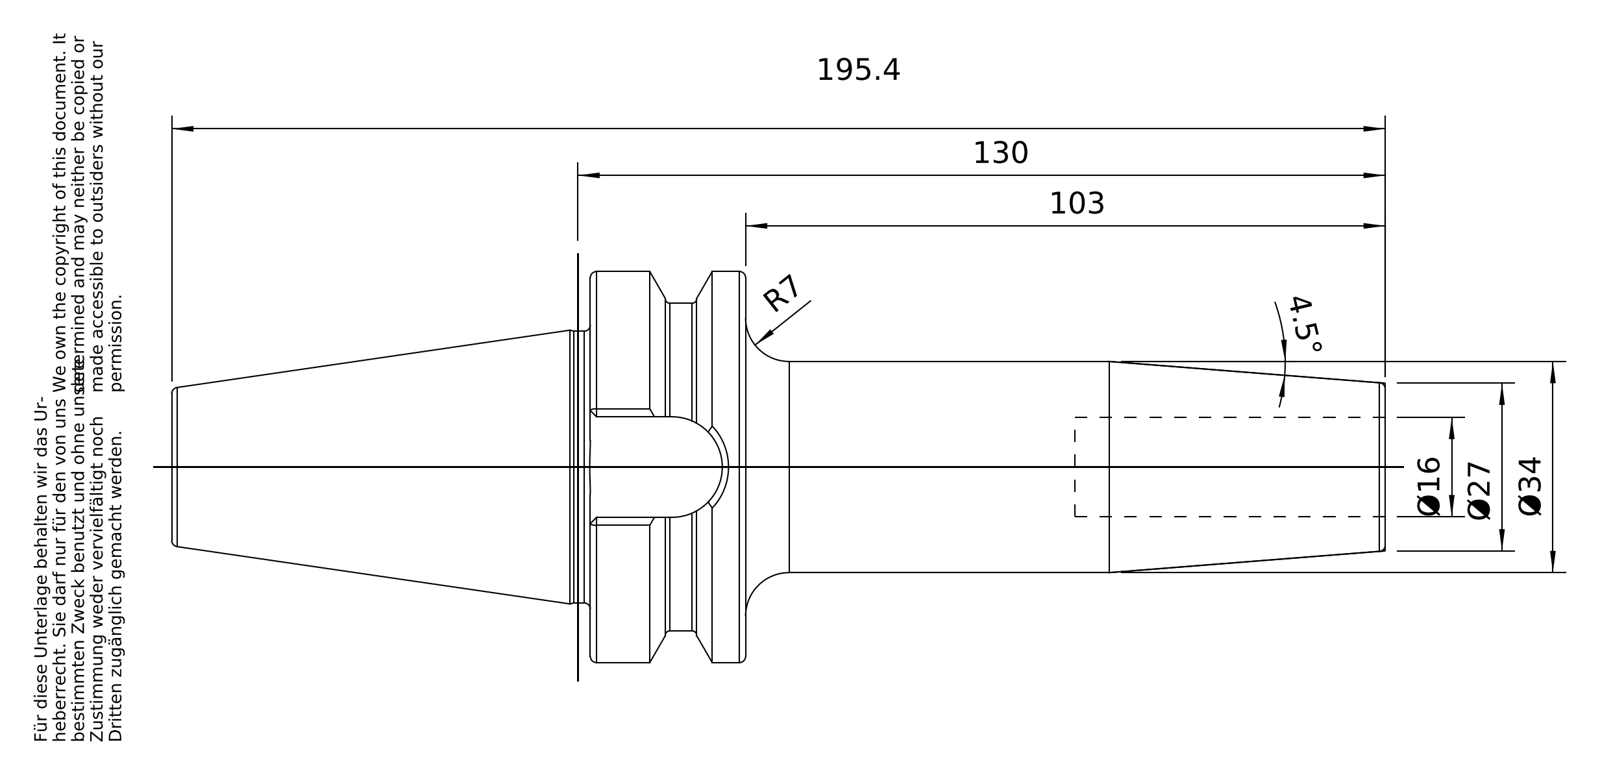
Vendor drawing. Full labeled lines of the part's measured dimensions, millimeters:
Part name (STEP PRODUCT): 40-644-16
STEP written by: PRO/ENGINEER BY PARAMETRIC TECHNOLOGY CORPORATION, 2010430 (CONFIG_CONTROL_DESIGN)
Units: millimetres
Bodies: 1 solid, 96 faces (26 planar, 22 cylindrical, 48 other)
Overall size (bounding box): 195.4 × 62.98 × 62.98
Volume: 203 074 mm³ · Surface area: 34 208 mm²
Round holes (diameter × count): ⌀13.84 ×1, ⌀16 ×1, ⌀17.01 ×1, ⌀17.5 ×1
Round bosses / shafts (diameter × count): ⌀62.98 ×1, ⌀52.75 ×1, ⌀43.75 ×1, ⌀34 ×1, ⌀16.01 ×1
Partial cylindrical surfaces — rounded edges, fillets, slot ends (radius × count): R8.1 ×1
Main face-to-face distances: 25, 44.9, 128, 103, 78, 53, 50, 16.2, 67.4, 92.4
